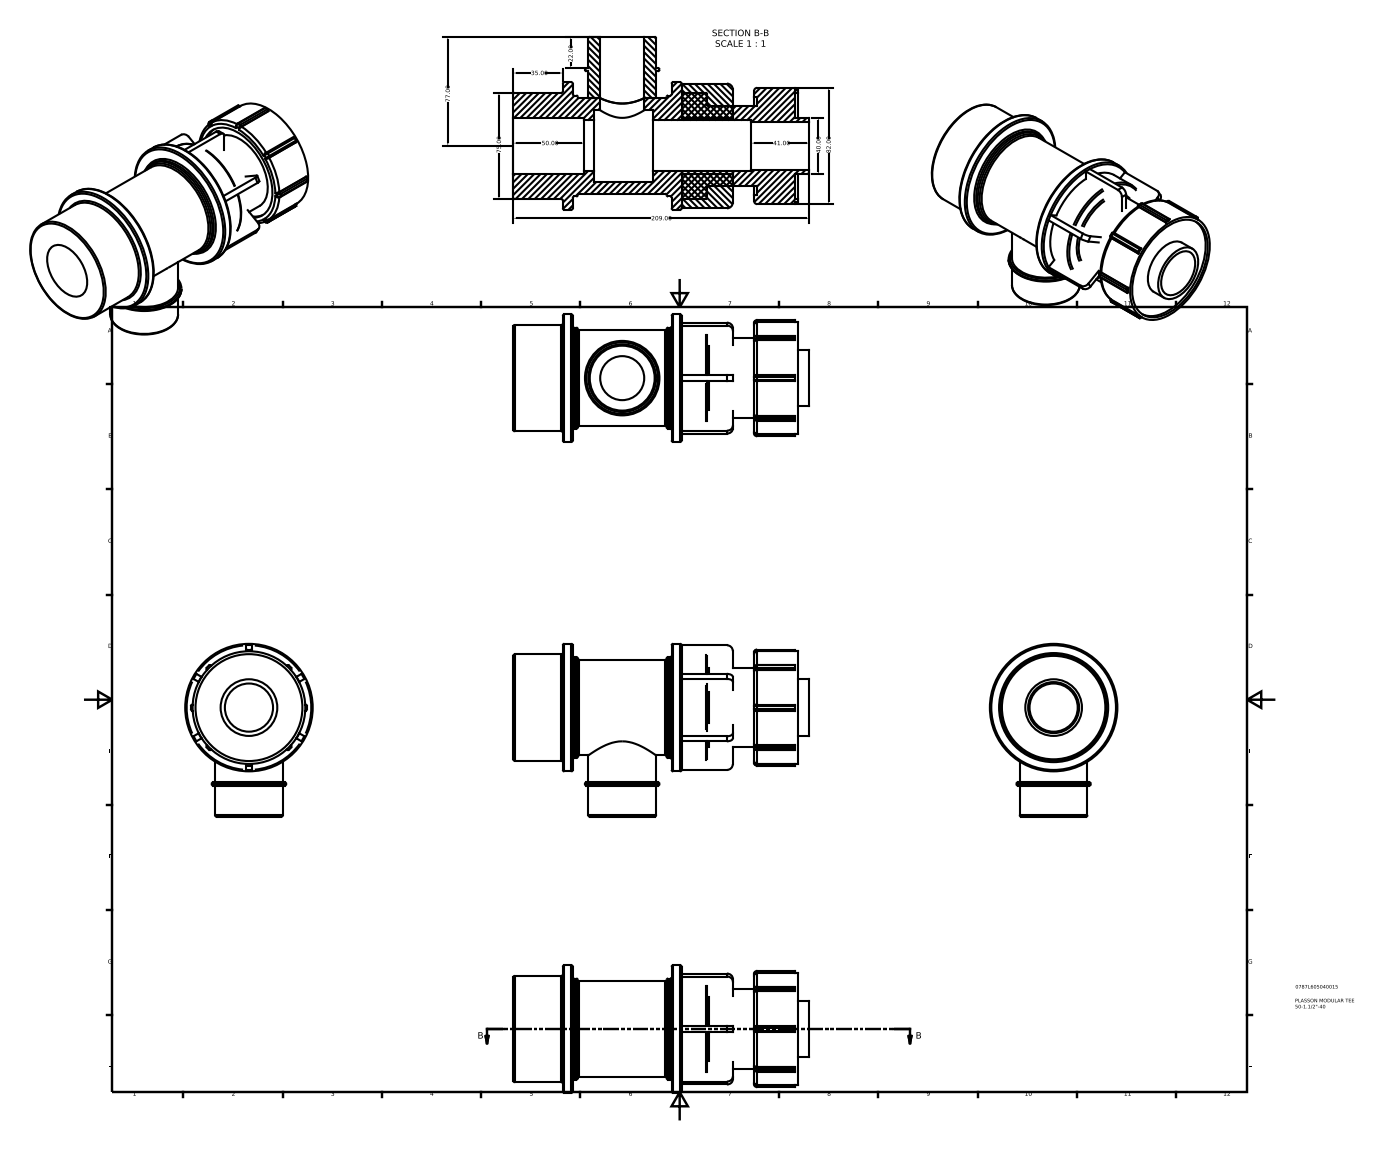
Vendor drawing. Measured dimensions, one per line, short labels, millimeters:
name: 0787L605040015
written by: Autodesk Inventor 2015 (AUTOMOTIVE_DESIGN)
unit: mm
bodies: 8 solids, 212 faces (86 planar, 69 cylindrical, 57 other)
size: 209 × 122 × 90
volume: 615 929 mm³; area: 122 566 mm²
holes: 1× ⌀31.07, 1× ⌀34, 1× ⌀36, 1× ⌀40, 1× ⌀50.4, 1× ⌀67.5, 1× ⌀69.7, 1× ⌀75.44
bosses: 1× ⌀90, 1× ⌀79.54, 1× ⌀75, 1× ⌀71.25, 1× ⌀56.25, 1× ⌀52.58, 1× ⌀47.8
rounds: 28× R1, 8× R2, 6× R4.1
face distances: 4.1, 76.8, 7, 198.75, 118.8, 79.95, 42, 156.75, 111.8, 69.8
